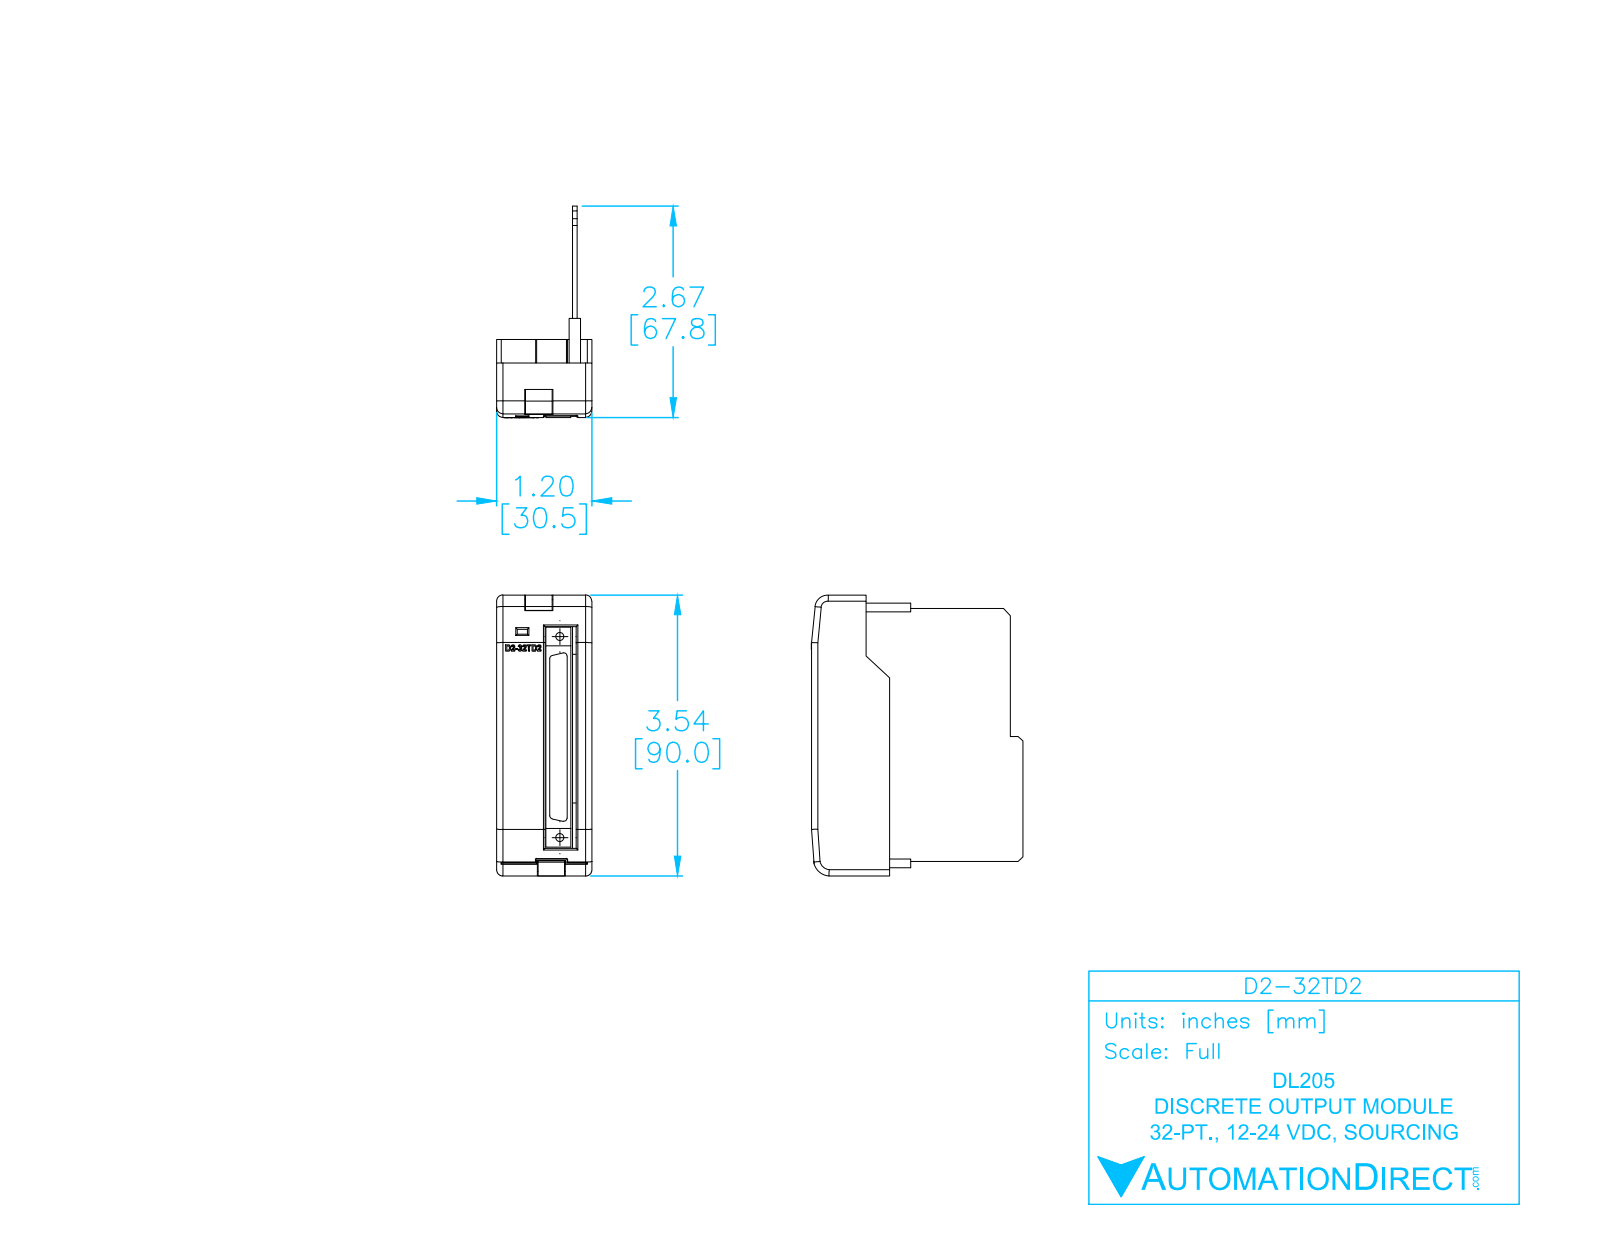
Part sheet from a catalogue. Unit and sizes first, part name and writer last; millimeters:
Units: millimetres
Overall size (bounding box): 90 × 67.85 × 30.5
Round holes (diameter × count): ⌀2.5 ×2
Partial cylindrical surfaces — rounded edges, fillets, slot ends (radius × count): R0.5 ×24, R2 ×10, R0.25 ×4, R1 ×4, R2.62 ×1, R3.79 ×1, R4.12 ×1, R5.29 ×1
Main face-to-face distances: 1.5, 4.72, 6.22, 3.22, 24.28, 29, 25.78, 30.5, 22.78, 27.5
Hole centre spacings: 64.38
Volume: 20 870 mm³ · Surface area: 29 166 mm²
Bodies: 5 solids, 325 faces (191 planar, 63 cylindrical, 71 other)
Part name (STEP PRODUCT): D2-32TD2_ModuleCase_light_NEW
STEP written by: SolidWorks 2009 (AUTOMOTIVE_DESIGN)
